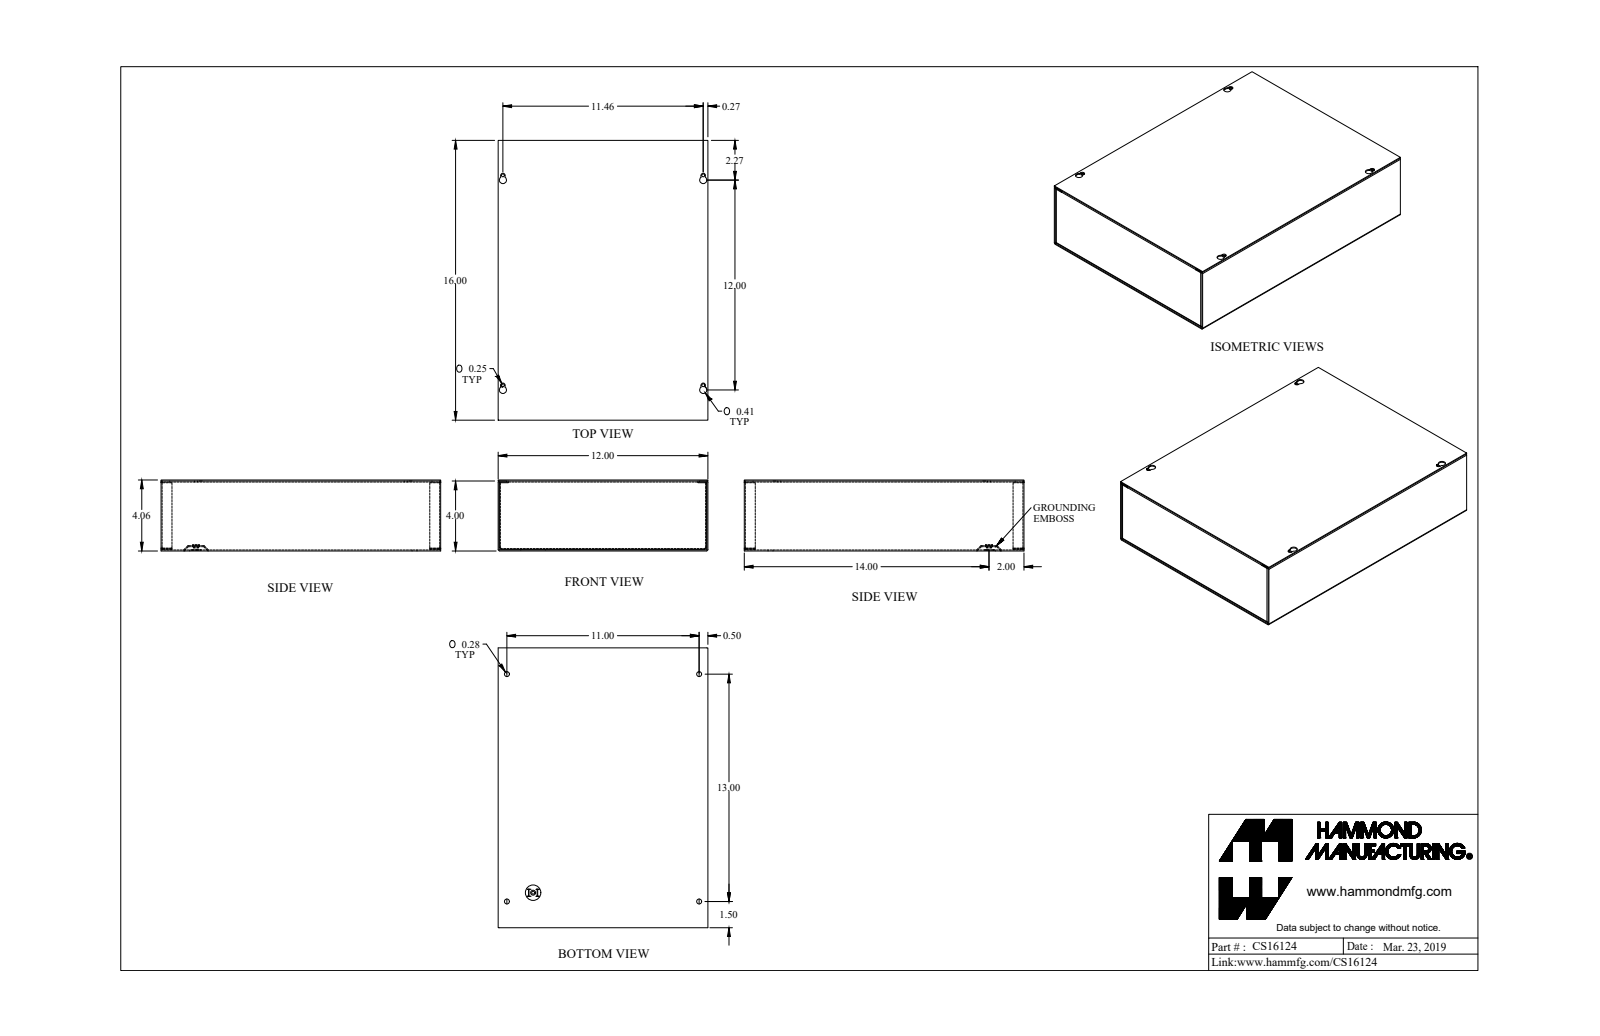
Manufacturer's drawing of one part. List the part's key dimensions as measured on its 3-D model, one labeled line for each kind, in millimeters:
Part name (STEP PRODUCT): CS16124_Default
STEP written by: SolidWorks 2019 (CONFIG_CONTROL_DESIGN)
Units: millimetres
Bodies: 4 solids, 205 faces (125 planar, 72 cylindrical, 8 other)
Overall size (bounding box): 406.4 × 304.8 × 103
Volume: 602 400 mm³ · Surface area: 840 000 mm²
Round holes (diameter × count): ⌀4.3 ×5, ⌀7.1 ×4, ⌀12.7 ×1
Round bosses / shafts (diameter × count): ⌀12.5 ×1, ⌀7.2 ×1
Partial cylindrical surfaces — rounded edges, fillets, slot ends (radius × count): R0.7 ×12, R2.2 ×12, R1.4 ×8, R3.2 ×4, R5.2 ×4
Main face-to-face distances: 1.4, 101.6, 100.2, 103, 303.4, 405, 304.8, 301.9, 406.4, 403.5
Hole centre spacings: 14, 285.5, 317.6, 426.8, 279.4, 291.1, 304.8, 330.2
